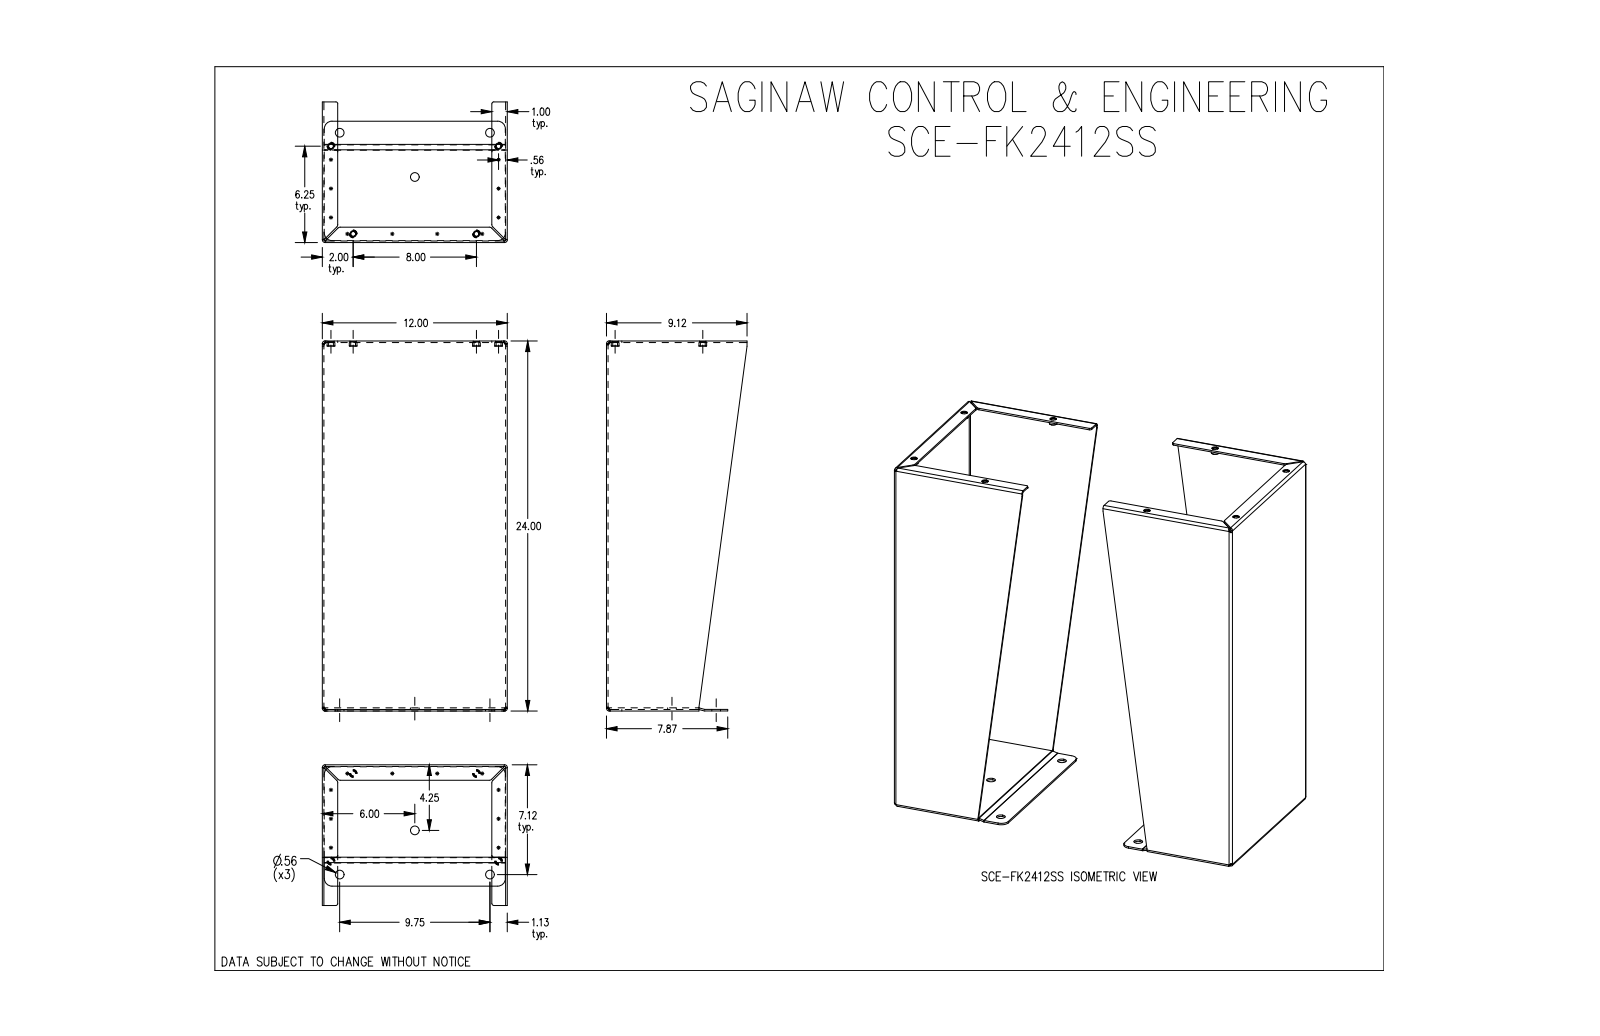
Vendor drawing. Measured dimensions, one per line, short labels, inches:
name: SCE-FK2412SS
written by: SolidWorks 2019 (CONFIG_CONTROL_DESIGN)
unit: in
bodies: 12 solids, 286 faces (120 planar, 110 cylindrical, 56 other)
size: 24 × 24 × 12
volume: 161.4 in³; area: 3 140 in²
holes: 8× ⌀0.312, 8× ⌀0.413, 6× ⌀0.563
bosses: 8× ⌀0.5, 8× ⌀0.412
rounds: 16× R0.166, 14× R0.062, 8× R0.125, 8× R0.22, 8× R0.5, 2× R0.063
face distances: 0.104, 11.896, 23.896, 23.792, 12, 11.792, 24, 0.101, 23.893, 23.688
hole spacings: 1.035, 5.441, 5.656, 5.793, 5.866, 6.614, 10.646, 11.019
